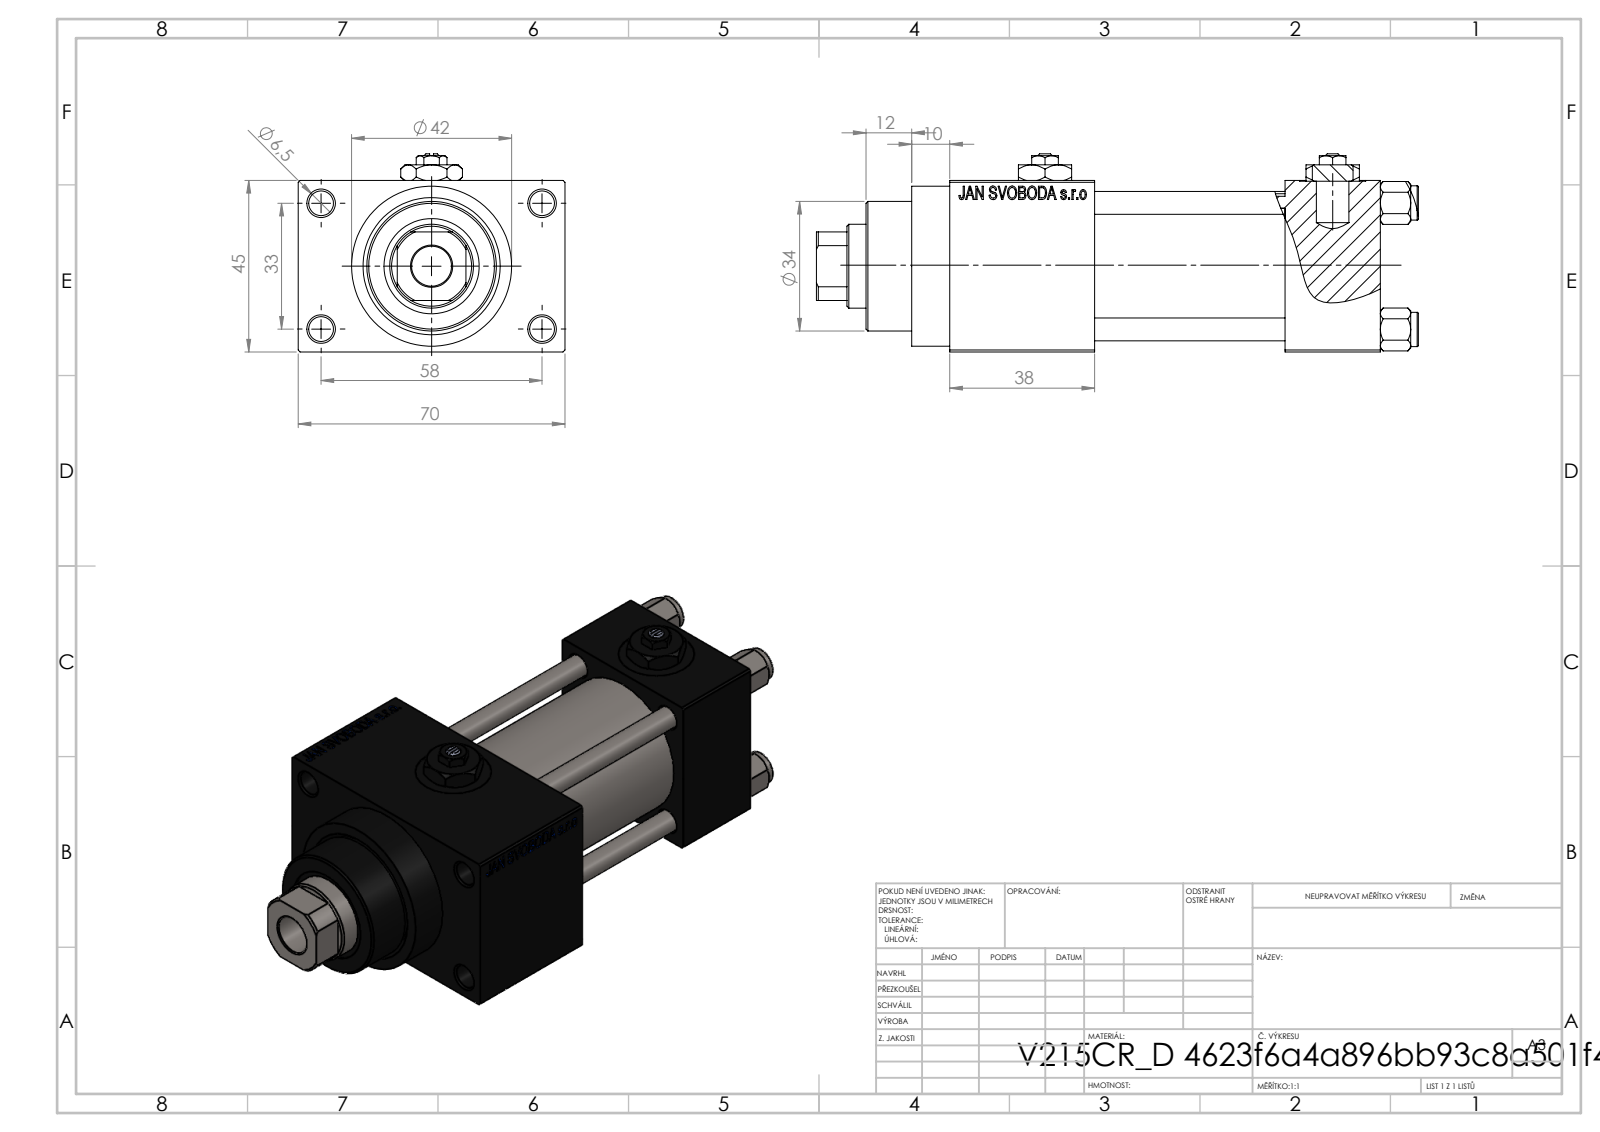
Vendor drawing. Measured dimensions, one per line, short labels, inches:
name: V215CR_D_Body; V215CR_D_TYCINKA; V215_VC_A; NUT_M5_D (+2 more)
written by: SolidWorks 2019 (CONFIG_CONTROL_DESIGN)
unit: in
bodies: 13 solids, 1203 faces (542 planar, 99 cylindrical, 562 other)
size: 6.22 × 2.756 × 2.047
volume: 14.74 in³; area: 126.5 in²
holes: 4× ⌀0.236, 4× ⌀0.256, 4× ⌀0.518, 4× ⌀0.787, 3× ⌀0.276, 1× ⌀0.413, 1× ⌀0.866, 1× ⌀0.945, 1× ⌀0.984, 1× ⌀1.26, 1× ⌀1.299
bosses: 4× ⌀0.354, 1× ⌀1.654, 1× ⌀1.496, 1× ⌀1.339
rounds: 1× R0.413
face distances: 1.772, 0.984, 1.969, 0.492, 2.953, 2.264, 3.465, 1.496, 4.449, 2.756
hole spacings: 0.488, 0.924, 1.307, 1.314, 1.392, 1.795, 2.219, 1.299
